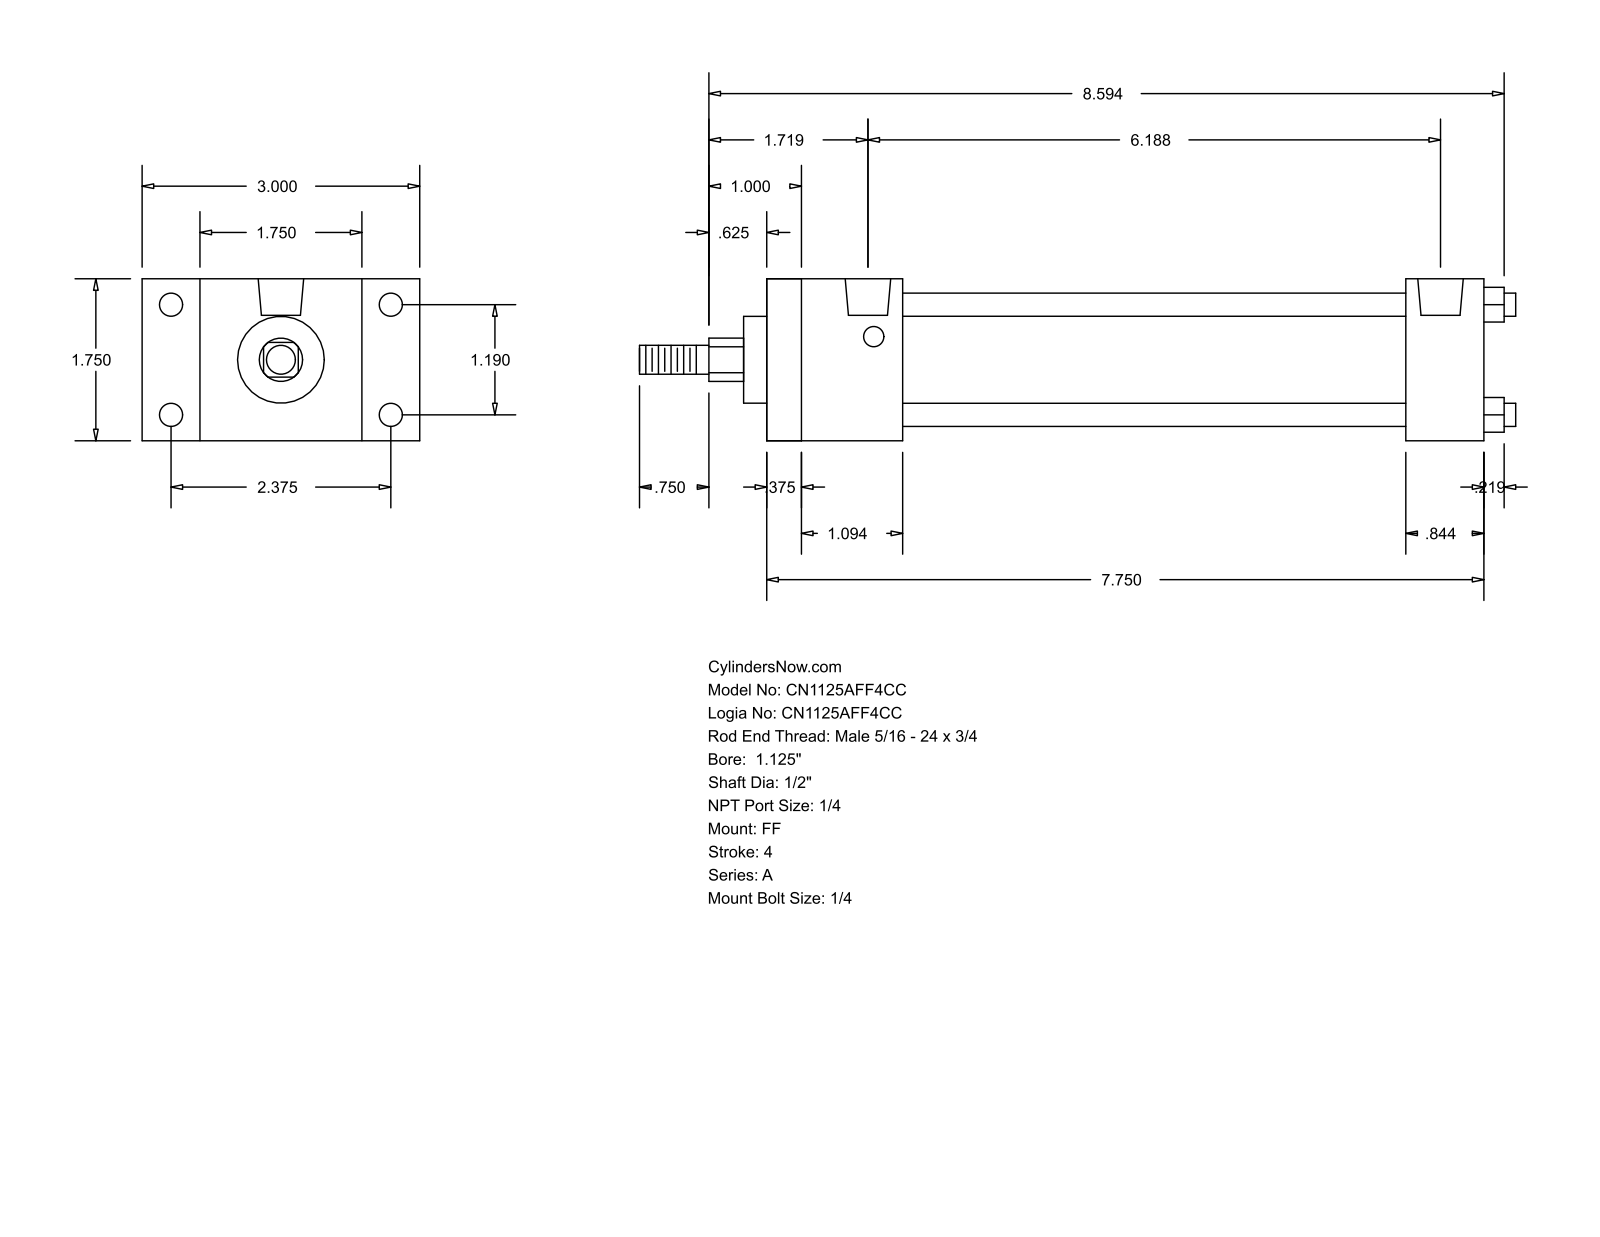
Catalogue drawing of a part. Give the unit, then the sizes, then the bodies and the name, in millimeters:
Units: millimetres
Overall size (bounding box): 240.51 × 76.2 × 44.45
Round holes (diameter × count): ⌀5.56 ×4, ⌀6.35 ×4, ⌀12.49 ×2
Round bosses / shafts (diameter × count): ⌀6.35 ×4, ⌀31.88 ×1, ⌀23.81 ×1, ⌀12.7 ×1, ⌀7.94 ×1
Partial cylindrical surfaces — rounded edges, fillets, slot ends (radius × count): R5.94 ×1
Main face-to-face distances: 44.46, 196.84, 9.52, 187.32, 15.87, 175.41, 165.89, 21.43, 37.3, 27.78
Hole centre spacings: 30.22, 60.32, 67.47, 153.99, 1.58, 1.59, 155.57, 155.58
Bodies: 0 solids, 92 faces (64 planar, 28 cylindrical, 0 other)
Part name (STEP PRODUCT): A_FF__0112_0.5
STEP written by: GSSL Pune (CONFIG_CONTROL_DESIGN)
